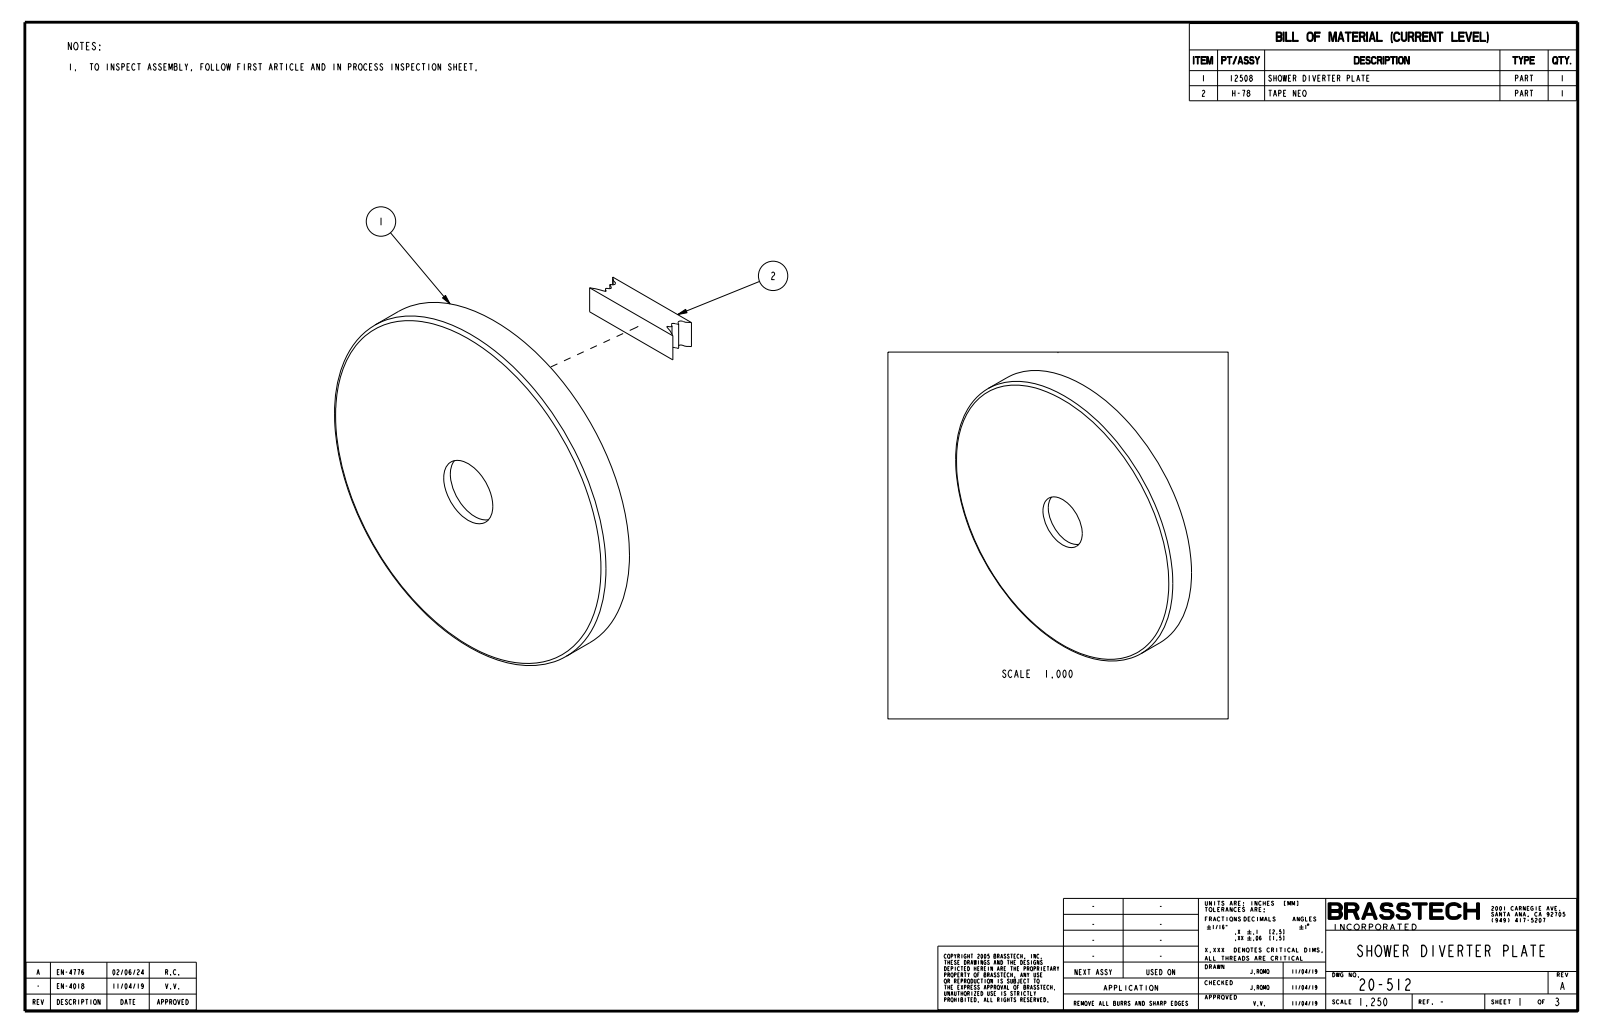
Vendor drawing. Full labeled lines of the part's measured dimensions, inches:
Part name (STEP PRODUCT): 12508; 20-512_ASM
STEP written by: CREO PARAMETRIC BY PTC INC, 2023134 (CONFIG_CONTROL_DESIGN)
Units: inches
Bodies: 1 solid, 18 faces (4 planar, 8 cylindrical, 6 other)
Overall size (bounding box): 3.25 × 3.25 × 0.313
Volume: 0.918 in³ · Surface area: 21.35 in²
Round holes (diameter × count): ⌀0.59 ×1, ⌀2.59 ×1, ⌀3.09 ×1
Round bosses / shafts (diameter × count): ⌀3.25 ×1
Main face-to-face distances: 0.08, 0.043, 0.122, 0.19, 0.233, 0.313
